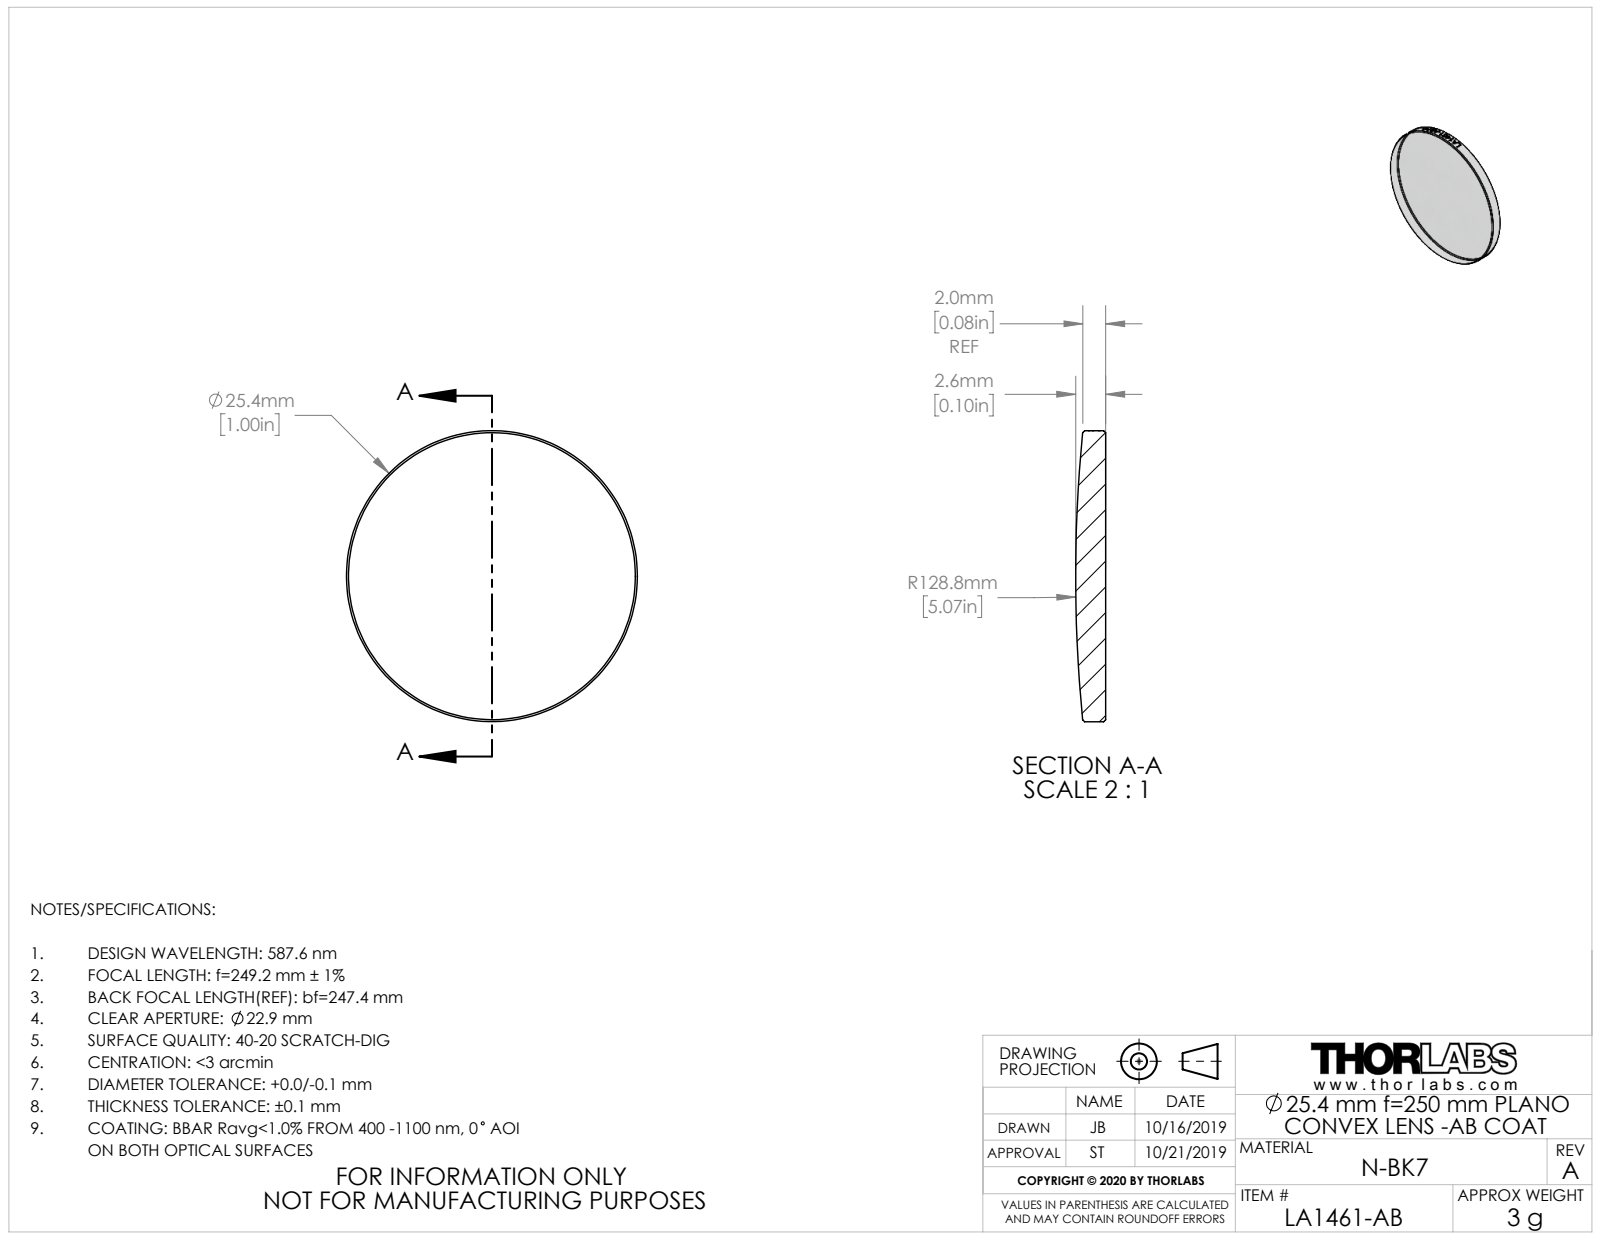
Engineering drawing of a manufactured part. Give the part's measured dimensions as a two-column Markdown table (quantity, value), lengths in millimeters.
| quantity | value |
| --- | --- |
| part name | TTN195778-E0W |
| STEP written by | SolidWorks 2018 (CONFIG_CONTROL_DESIGN) |
| units | millimeters |
| bodies | 1 solid, 28 faces (1 planar, 21 cylindrical, 6 other) |
| overall size | 25.4 × 25.4 × 2.6 |
| volume | 1 200 mm³ |
| surface area | 1 158 mm² |
| round bosses / shafts (diameter × count) | 25.4 × 1 |
